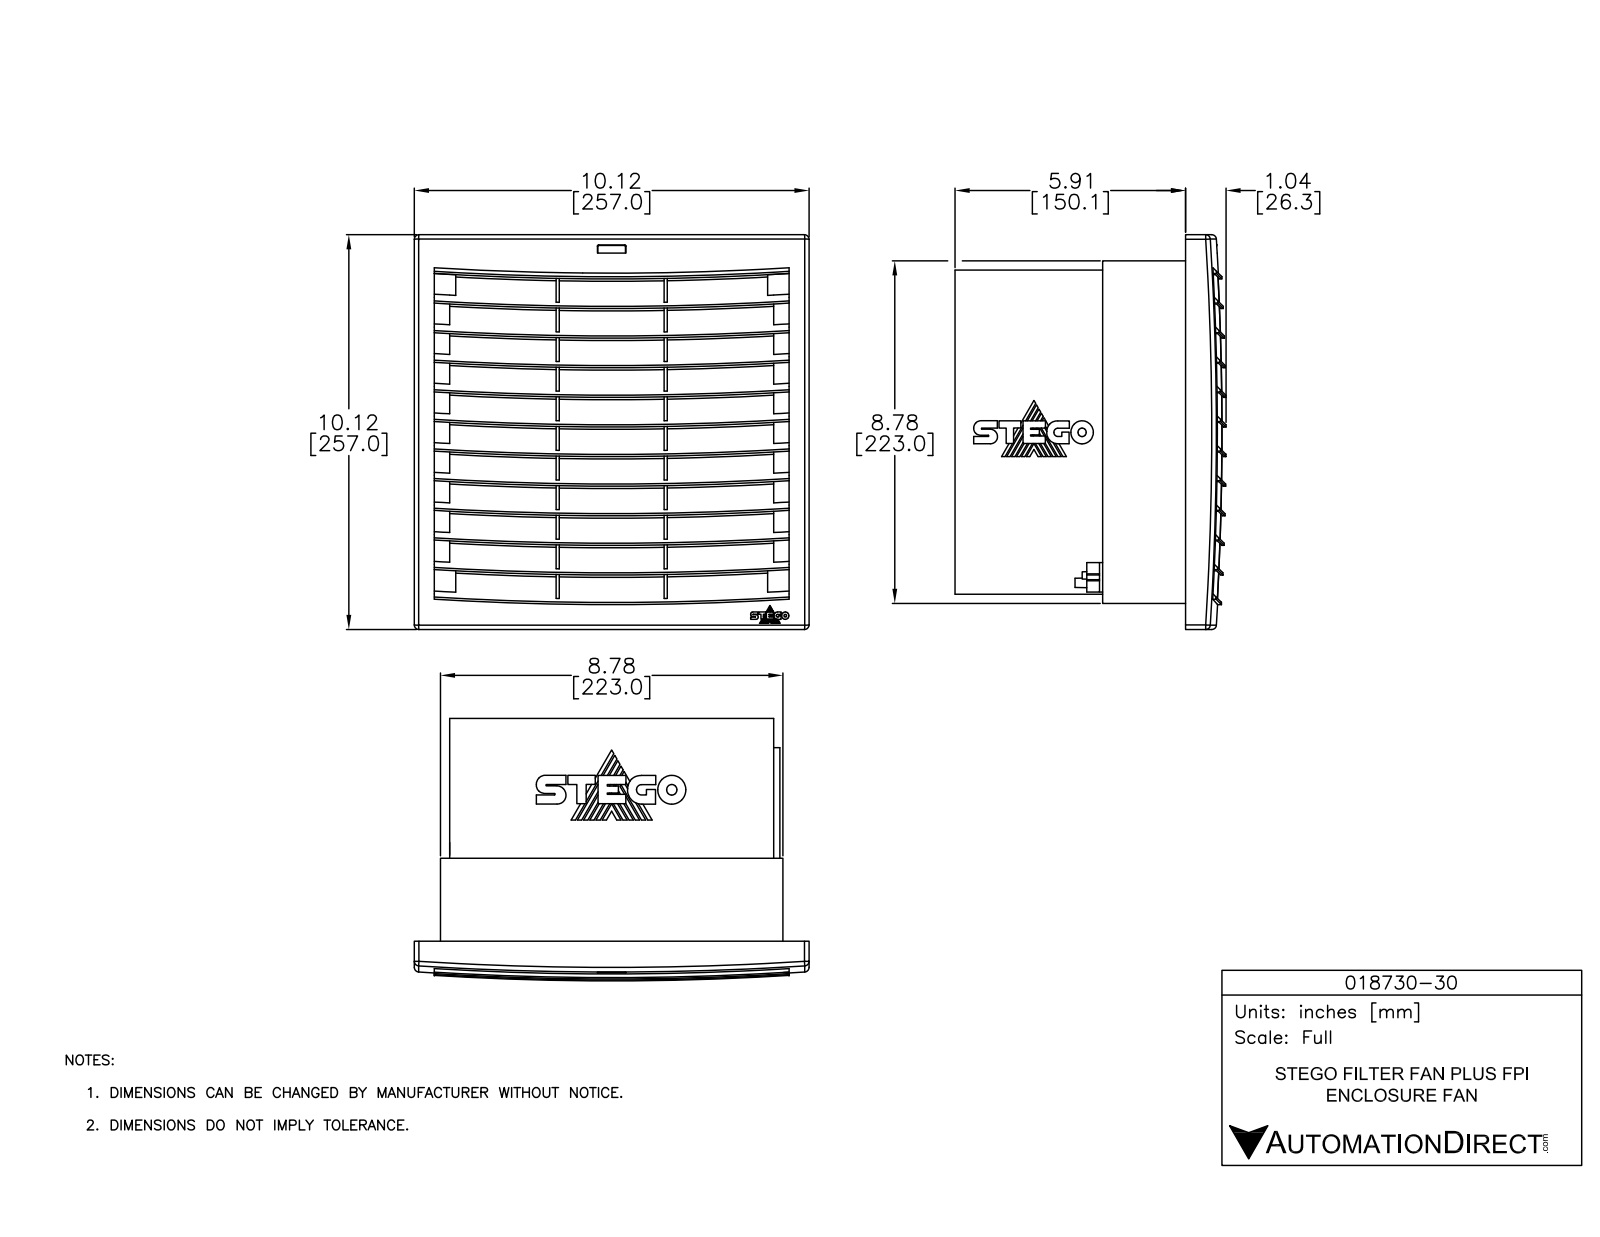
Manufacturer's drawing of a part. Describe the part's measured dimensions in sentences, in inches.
The part is named "018730-30". Its 3-D file was written by "SolidWorks 2018 (AUTOMOTIVE_DESIGN)". It is 1 solid with 814 faces: 468 planar, 346 cylindrical and 0 other. Overall it measures 10.118 by 10.118 by 6.811 inches. Its volume is 192.8 cubic inches and its surface area 1 039 square inches. Round holes: 1 of diameter 2.268, 1 of diameter 3.018, 1 of diameter 3.769, 1 of diameter 4.487, 1 of diameter 4.52, 1 of diameter 5.27, 1 of diameter 5.42, 1 of diameter 6.021, 1 of diameter 6.353, 1 of diameter 6.929, 1 of diameter 7.463. Round bosses or shafts: 1 of diameter 8.64, 1 of diameter 8.228, 1 of diameter 8.146, 1 of diameter 6.707, 1 of diameter 6.336, 1 of diameter 5.774, 1 of diameter 5.585, 1 of diameter 4.841. Partial cylindrical surfaces (rounded edges, fillets, slot ends): 21 of radius 42.577, 5 of radius 3.361, 4 of radius 0.197, 4 of radius 0.26, 1 of radius 0.933, 1 of radius 1.311, 1 of radius 1.488, 1 of radius 1.777. The main face-to-face distances are 0.536, 0.059, 0.543, 2.145, 2.681, 1.609, 0.22, 8.56, 1.073, 1.072.
